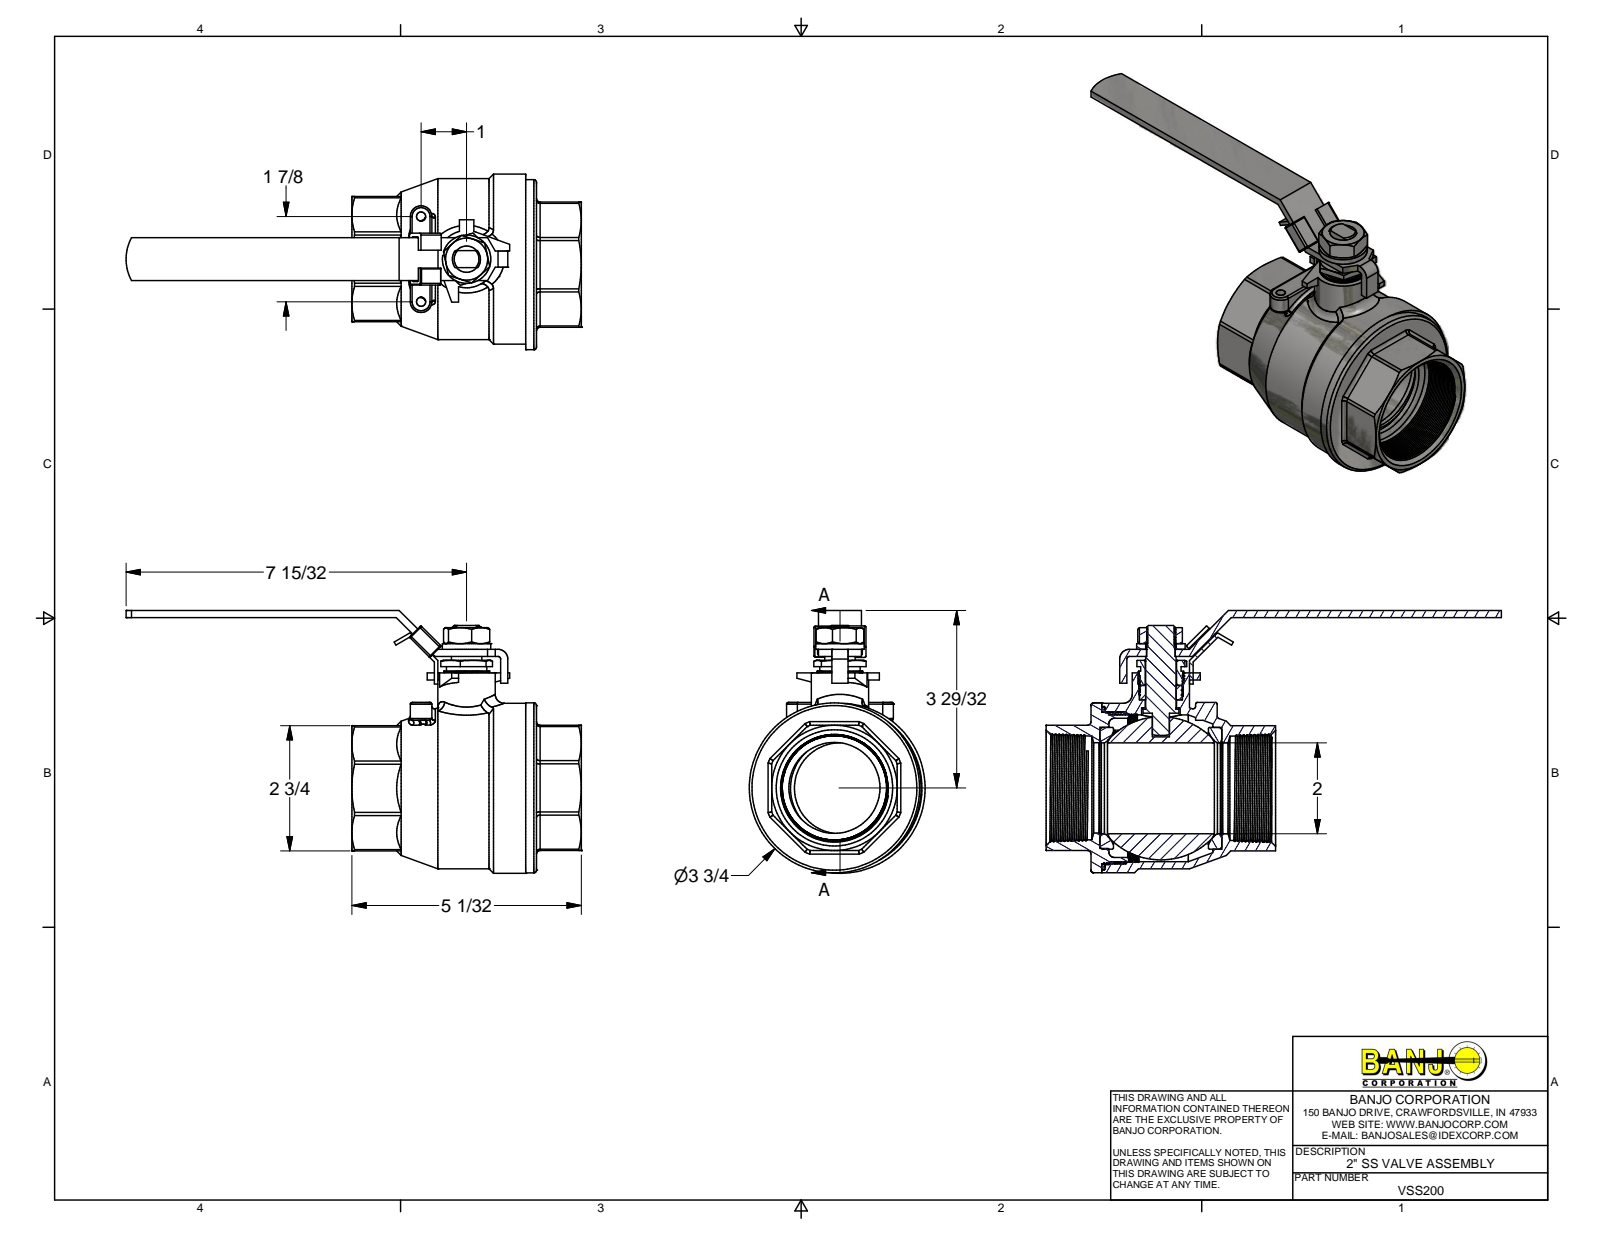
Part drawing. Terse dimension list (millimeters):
name: VSS200; PG; GT; BY (+8 more)
written by: Autodesk Inventor 2013 (AUTOMOTIVE_DESIGN)
unit: mm
bodies: 14 solids, 502 faces (150 planar, 150 cylindrical, 202 other)
size: 254 × 146.9 × 98.1
volume: 402 802 mm³; area: 158 672 mm²
holes: 2× ⌀5.11, 2× ⌀50.8, 1× ⌀14.68, 1× ⌀17, 1× ⌀17.5, 1× ⌀21.5, 1× ⌀24, 1× ⌀68, 1× ⌀78, 1× ⌀82, 1× ⌀85, 1× ⌀85.5
bosses: 2× ⌀95, 1× ⌀90.5, 1× ⌀90, 1× ⌀85, 1× ⌀68, 1× ⌀32, 1× ⌀27, 1× ⌀25.4
rounds: 20× R1, 8× R2, 7× R0.5, 2× R6, 2× R25, 2× R37.5, 1× R1.5, 1× R5.5
face distances: 4, 5, 2.5, 68, 1, 70, 69.99, 67, 2, 6
hole spacings: 3.11, 34.81, 34.82, 47.63
